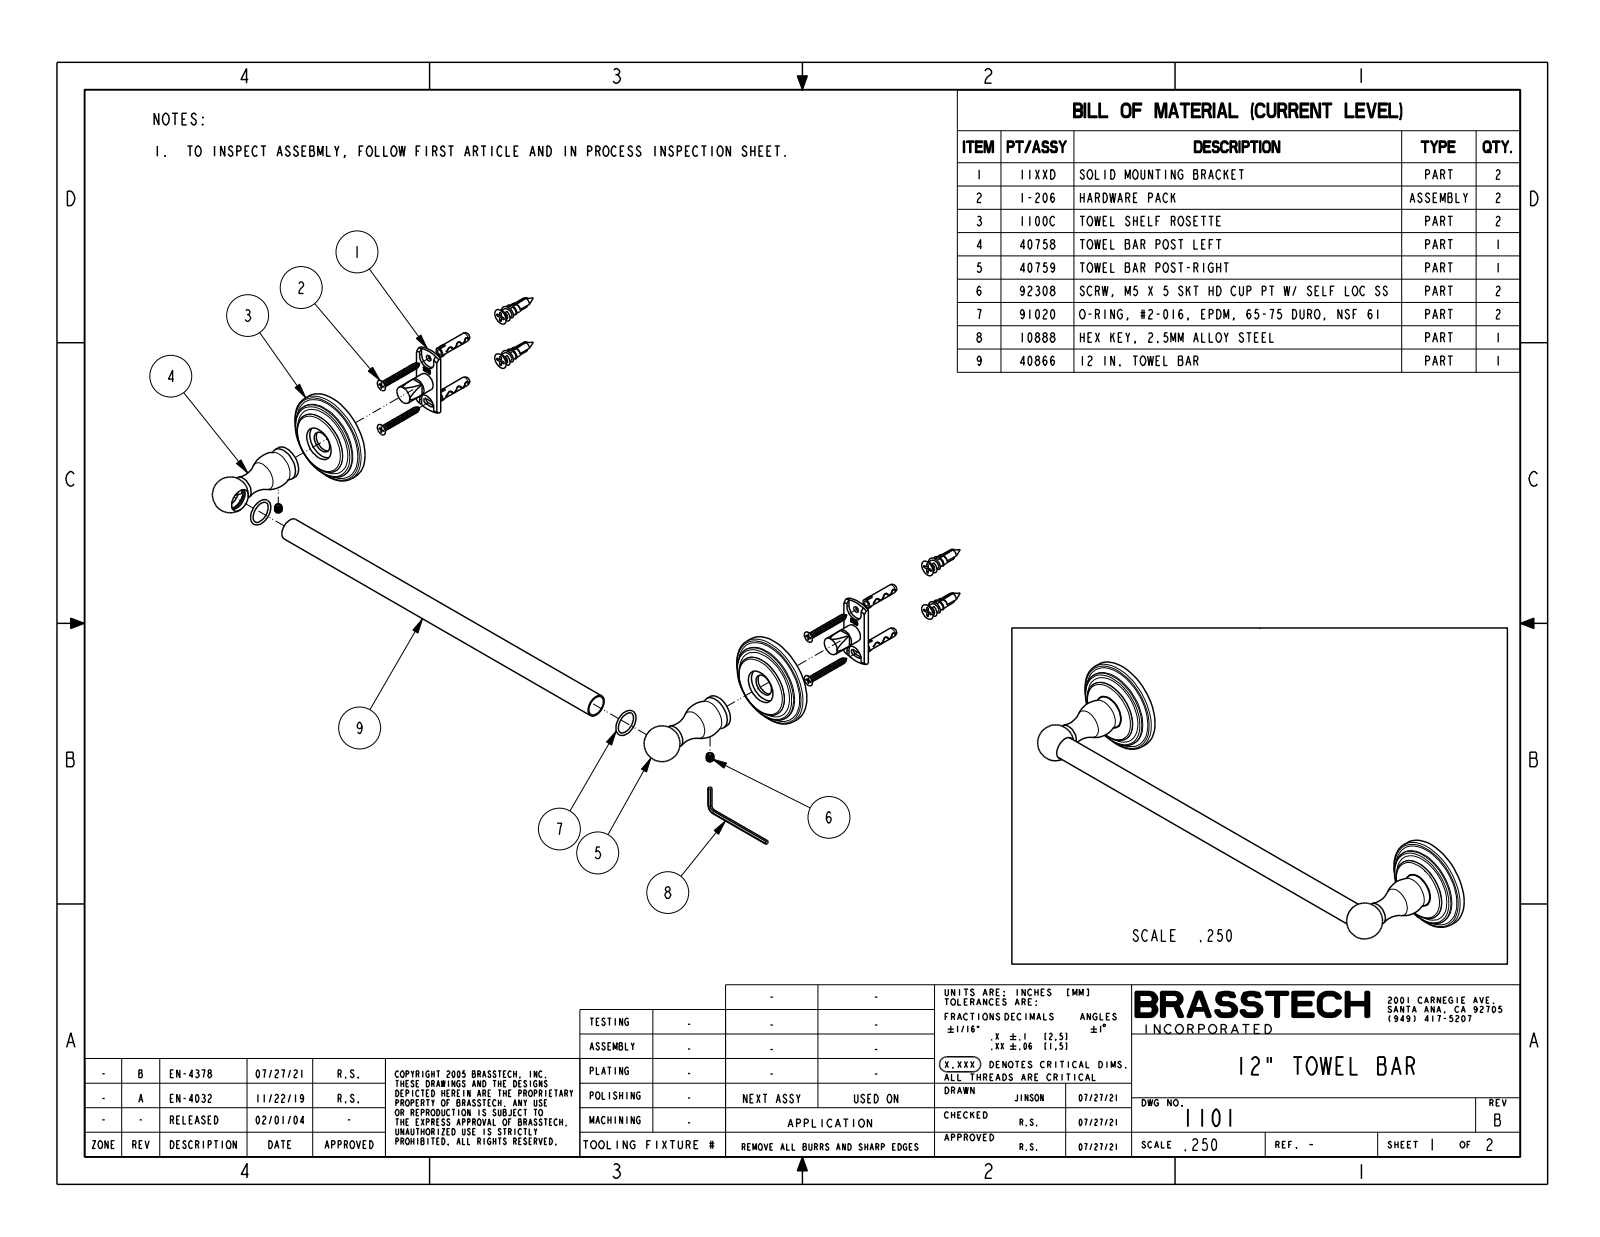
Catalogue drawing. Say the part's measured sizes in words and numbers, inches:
The part is named "1101". Its 3-D file was written by "CREO PARAMETRIC BY PTC INC, 2018400 (CONFIG_CONTROL_DESIGN)". It is 1 solid with 72 faces: 10 planar, 22 cylindrical and 40 other. Overall it measures 14.56 by 3.075 by 2.56 inches. Its volume is 9.99 cubic inches and its surface area 60.84 square inches. Round holes: 1 of diameter 0.65. Round bosses or shafts: 2 of diameter 2.56, 2 of diameter 2.182, 2 of diameter 1.748, 2 of diameter 0.928, 1 of diameter 0.625. The main face-to-face distances are 0.512, 0.362, 0.15, 0.189, 0.173, 0.323, 11.51.
